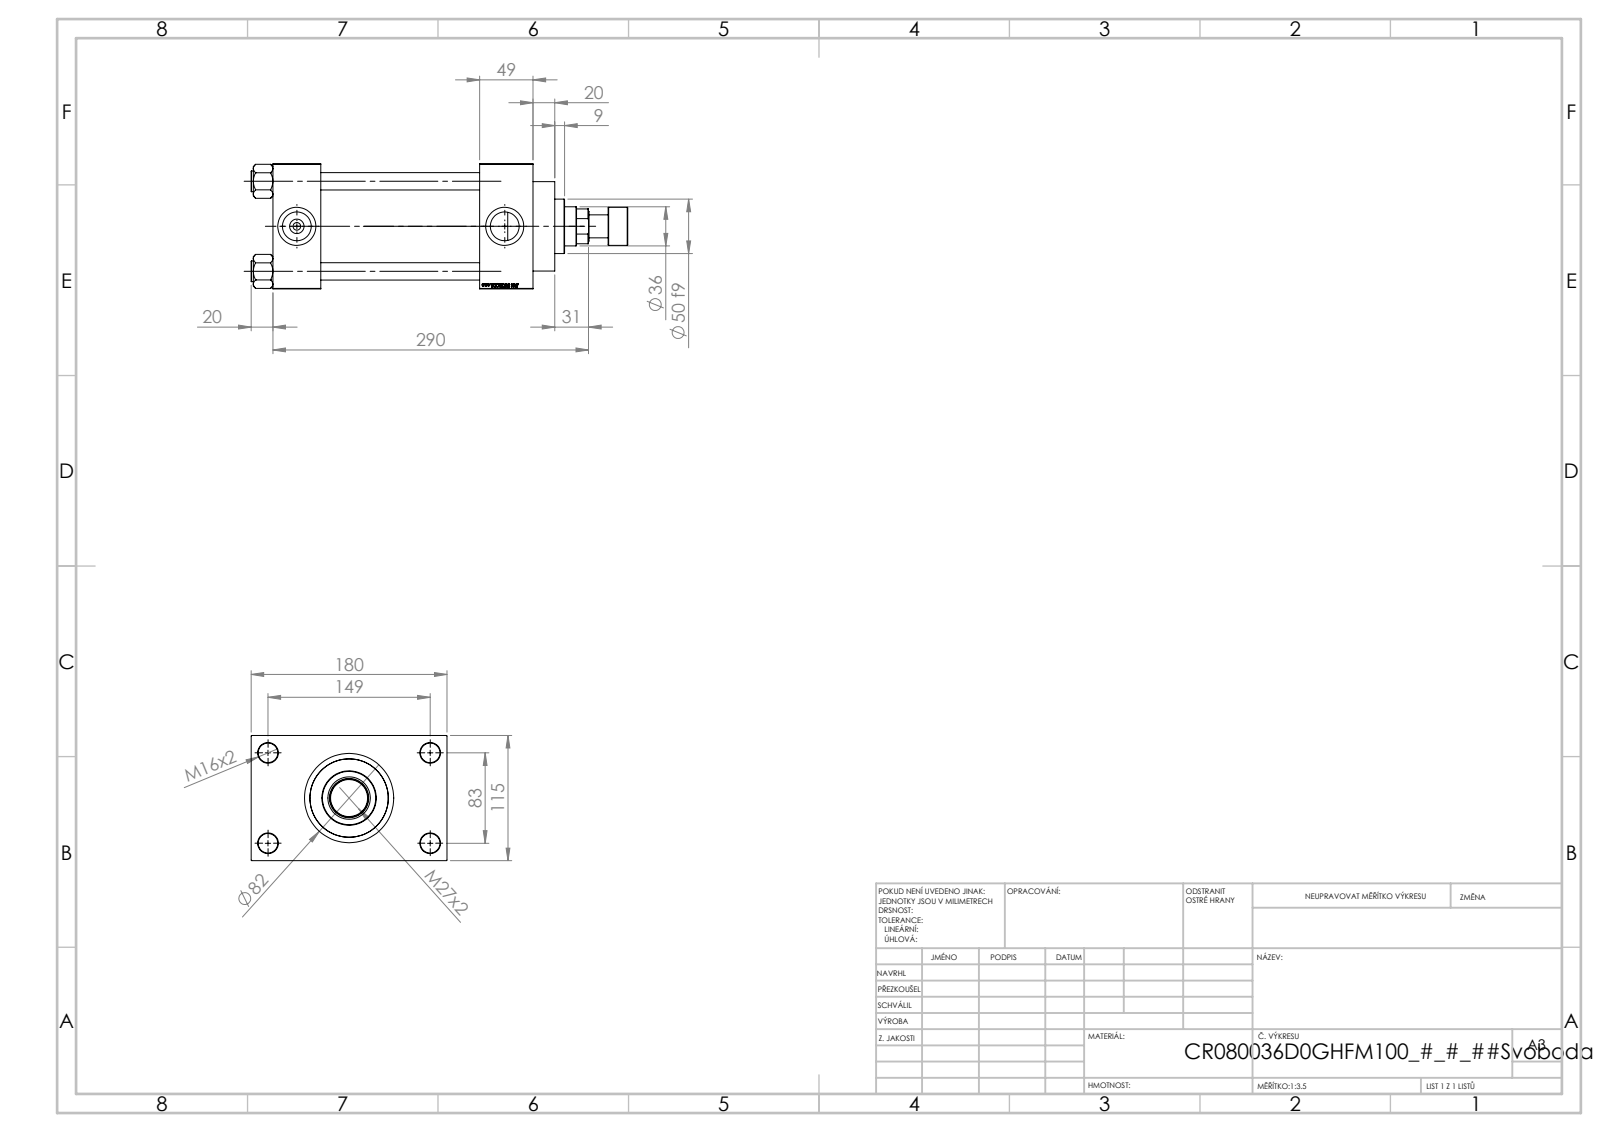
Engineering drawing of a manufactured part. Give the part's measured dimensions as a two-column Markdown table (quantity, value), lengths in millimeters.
| quantity | value |
| --- | --- |
| part name | V215CR_D_TYCINKA; V215CR_VCP_D; V215CR_D_Body; V215CR_ROD_END_F (+2 more) |
| STEP written by | SolidWorks 2019 (CONFIG_CONTROL_DESIGN) |
| units | millimeters |
| bodies | 12 solids, 1165 faces (549 planar, 92 cylindrical, 524 other) |
| overall size | 346 × 180 × 115 |
| volume | 2 211 000 mm³ |
| surface area | 369 014 mm² |
| round holes (diameter × count) | 16 × 4, 18 × 4, 7 × 2, 26.44 × 2, 35 × 2, 25.5 × 1, 36 × 1, 39 × 1, 61 × 1, 72 × 1, 80 × 1 |
| round bosses / shafts (diameter × count) | 19 × 4, 86 × 1, 82 × 1, 50 × 1, 35 × 1, 21 × 1 |
| main face-to-face distances | 115, 146, 49, 195, 44, 190, 239, 32.5, 147.5, 100 |
| hole center spacings | 33.15, 58.48, 82.7, 85.28, 89.24, 115.85, 142.43, 83 |
